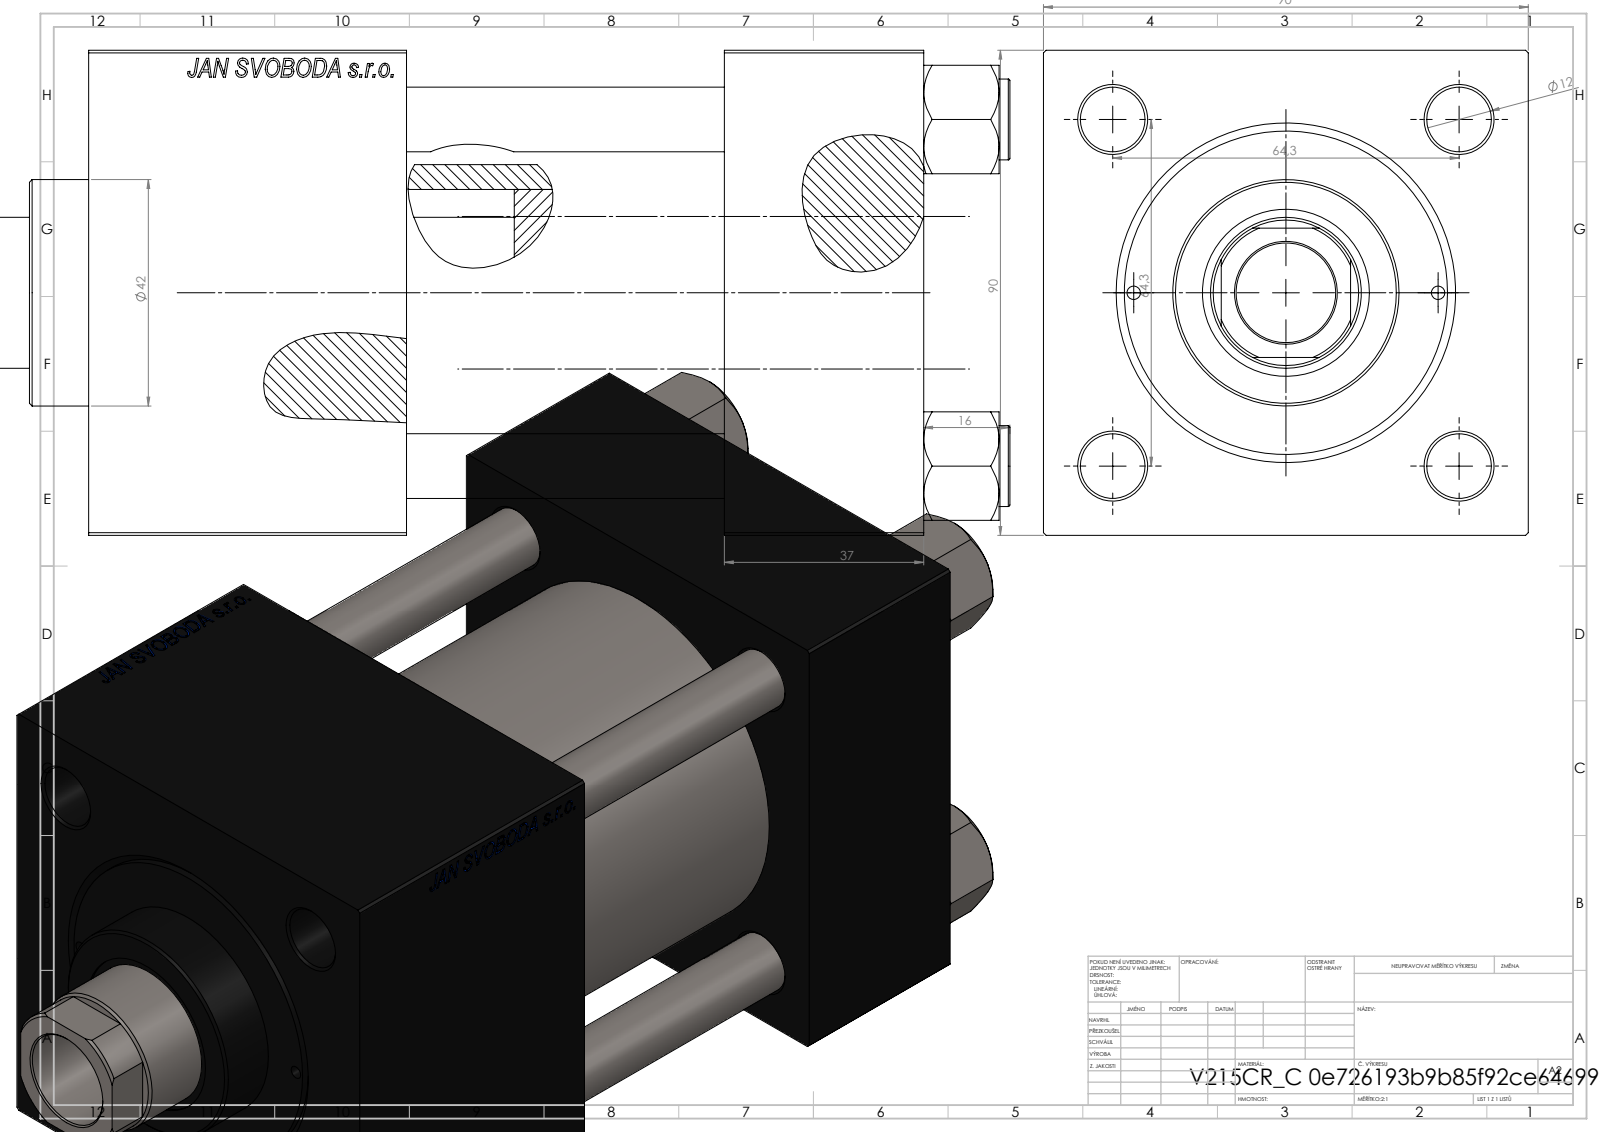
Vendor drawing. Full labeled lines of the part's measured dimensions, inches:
Part name (STEP PRODUCT): V215CR_VCP_C; V215CR_C_Body; V215_VC_A; V215CR_C_TYCINKA (+1 more)
STEP written by: SolidWorks 2019 (CONFIG_CONTROL_DESIGN)
Units: inches
Bodies: 11 solids, 1154 faces (528 planar, 90 cylindrical, 536 other)
Overall size (bounding box): 7.992 × 3.543 × 3.543
Volume: 57.78 in³ · Surface area: 277.8 in²
Round holes (diameter × count): ⌀0.472 ×4, ⌀0.098 ×2, ⌀0.276 ×2, ⌀0.825 ×2, ⌀1.181 ×2, ⌀0.728 ×1, ⌀1.102 ×1, ⌀1.22 ×1, ⌀1.969 ×1, ⌀2.362 ×1, ⌀2.48 ×1
Round bosses / shafts (diameter × count): ⌀0.591 ×4, ⌀2.717 ×1, ⌀1.654 ×1
Partial cylindrical surfaces — rounded edges, fillets, slot ends (radius × count): R0.531 ×1
Main face-to-face distances: 3.543, 2.323, 1.457, 6.102, 4.646, 3.78, 4.972, 3.516, 1.193, 1.13
Hole centre spacings: 1.275, 1.79, 2.531, 2.694, 1.112, 3.58, 2.224, 3.839
